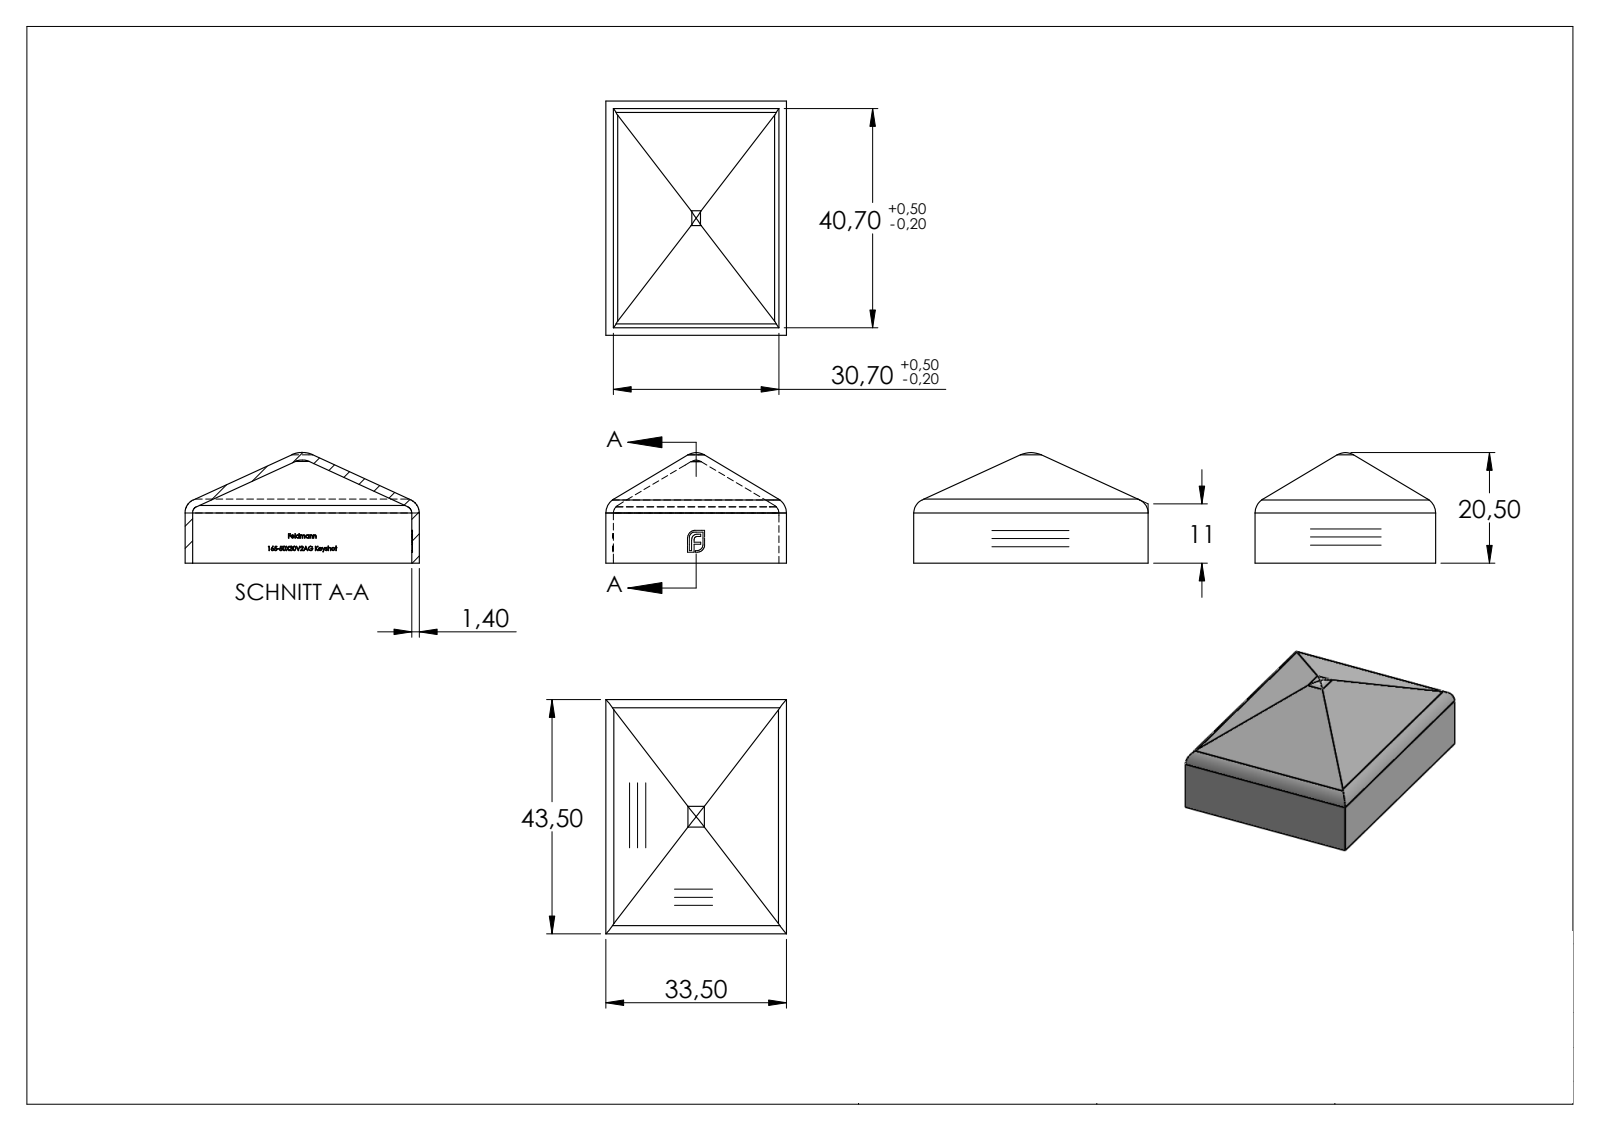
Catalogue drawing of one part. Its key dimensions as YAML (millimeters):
part_name: "165-40X30V4AG"
step_written_by: "SolidWorks 2018 (CONFIG_CONTROL_DESIGN)"
units: millimeters
bodies: {solids: 1, faces: 346, planar: 204, cylindrical: 16, other: 126}
overall_size: [43.5, 33.5, 20.5]
volume: 4285
surface_area: 6347
partial_cylinders:
  - {radius: 1.6, count: 3}
  - {radius: 3, count: 3}
  - {radius: 1.25, count: 2}
  - {radius: 2.65, count: 2}
  - {radius: 3.26, count: 1}
  - {radius: 4.66, count: 1}
face_to_face_distances: [1.4, 32.1, 42.1, 33.5, 30.7, 43.5, 40.7, 1.3, 40.8, 42.2]
